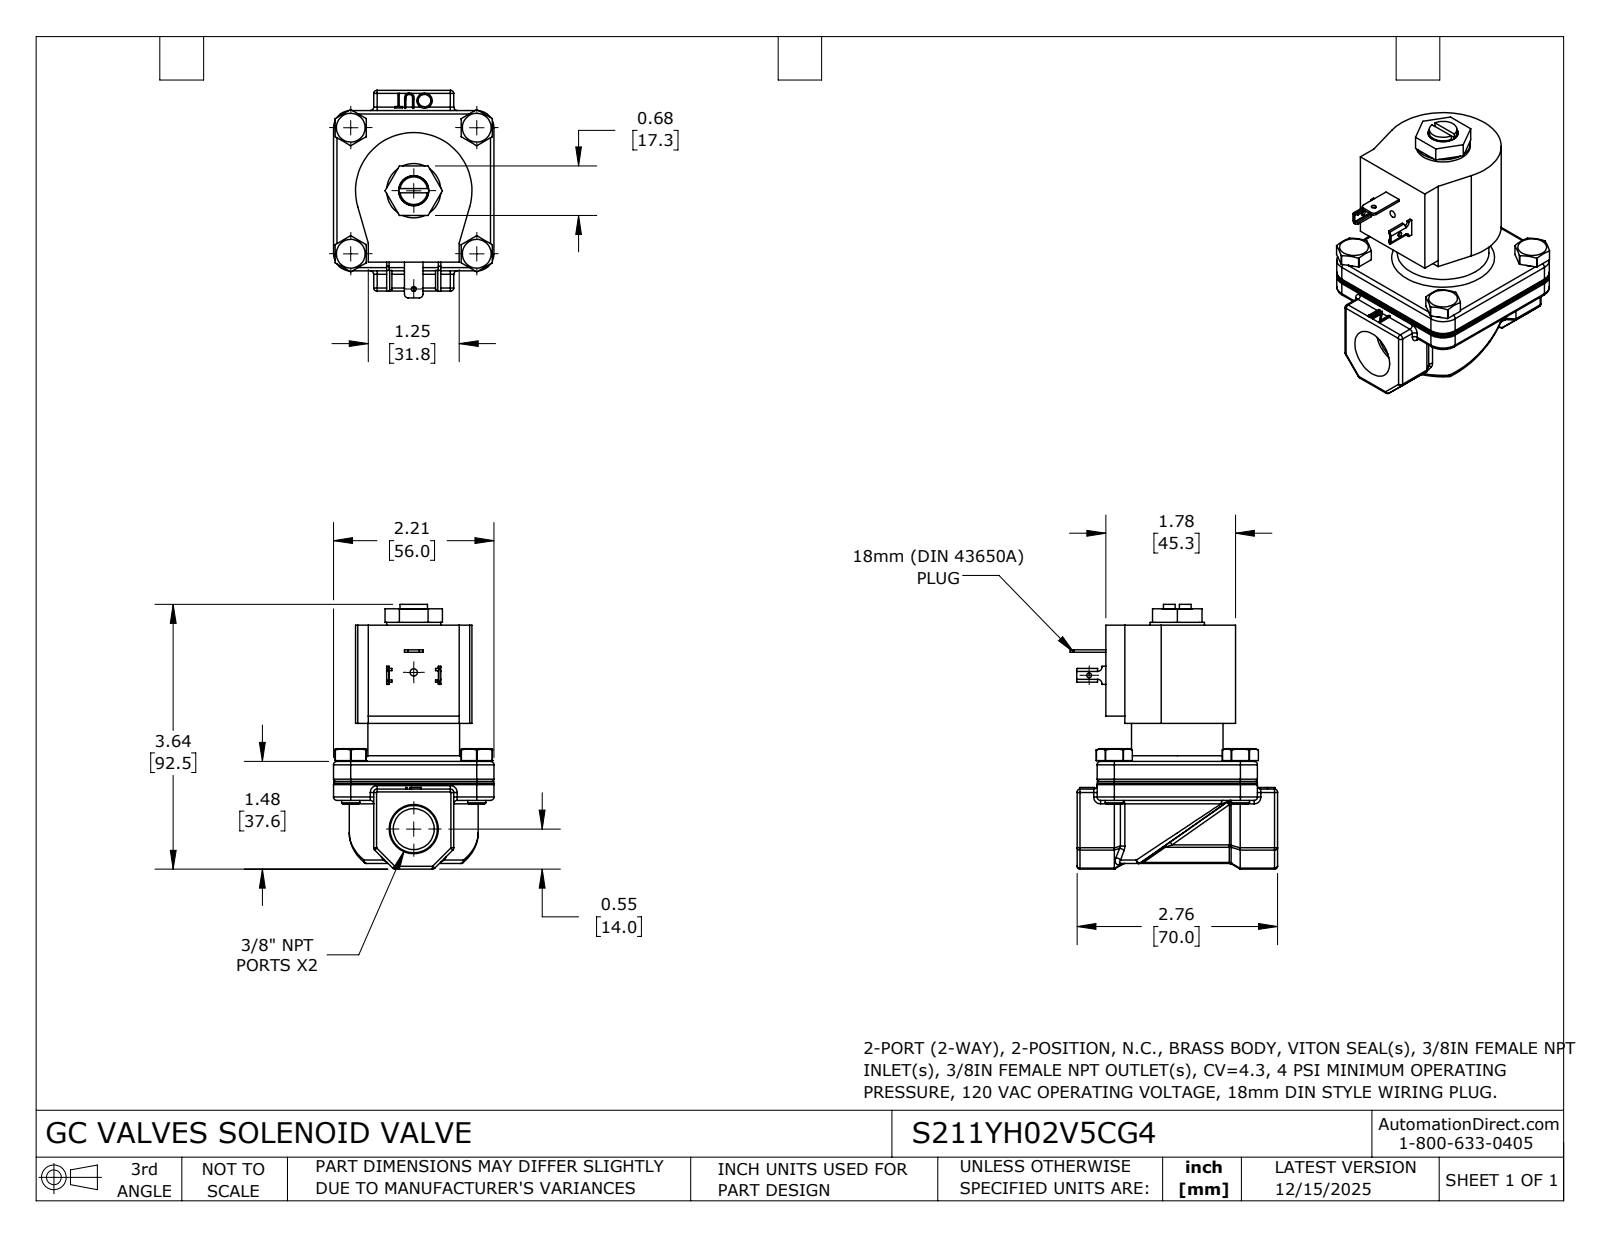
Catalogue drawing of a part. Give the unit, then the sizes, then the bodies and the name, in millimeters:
Units: millimetres
Overall size (bounding box): 92.5 × 72.4 × 56
Round holes (diameter × count): ⌀1.7 ×1, ⌀1.7 ×1, ⌀2.5 ×1, ⌀14.3 ×1
Round bosses / shafts (diameter × count): ⌀10.3 ×4, ⌀6.4 ×4, ⌀32 ×1, ⌀18.9 ×1, ⌀9.7 ×1
Partial cylindrical surfaces — rounded edges, fillets, slot ends (radius × count): R1.2 ×57, R1 ×12, R0.2 ×4, R0.8 ×4, R1 ×4, R5.9 ×4, R6 ×4, R1.3 ×2
Main face-to-face distances: 47.6, 14, 42, 56, 13.6, 61.2, 7, 63, 26.9, 13.3
Hole centre spacings: 54.7
Volume: 150 200 mm³ · Surface area: 25 060 mm²
Bodies: 1 solid, 507 faces (228 planar, 151 cylindrical, 128 other)
Part name (STEP PRODUCT): S211YH02V5CG4
STEP written by: SolidWorks 2024 (CONFIG_CONTROL_DESIGN)
